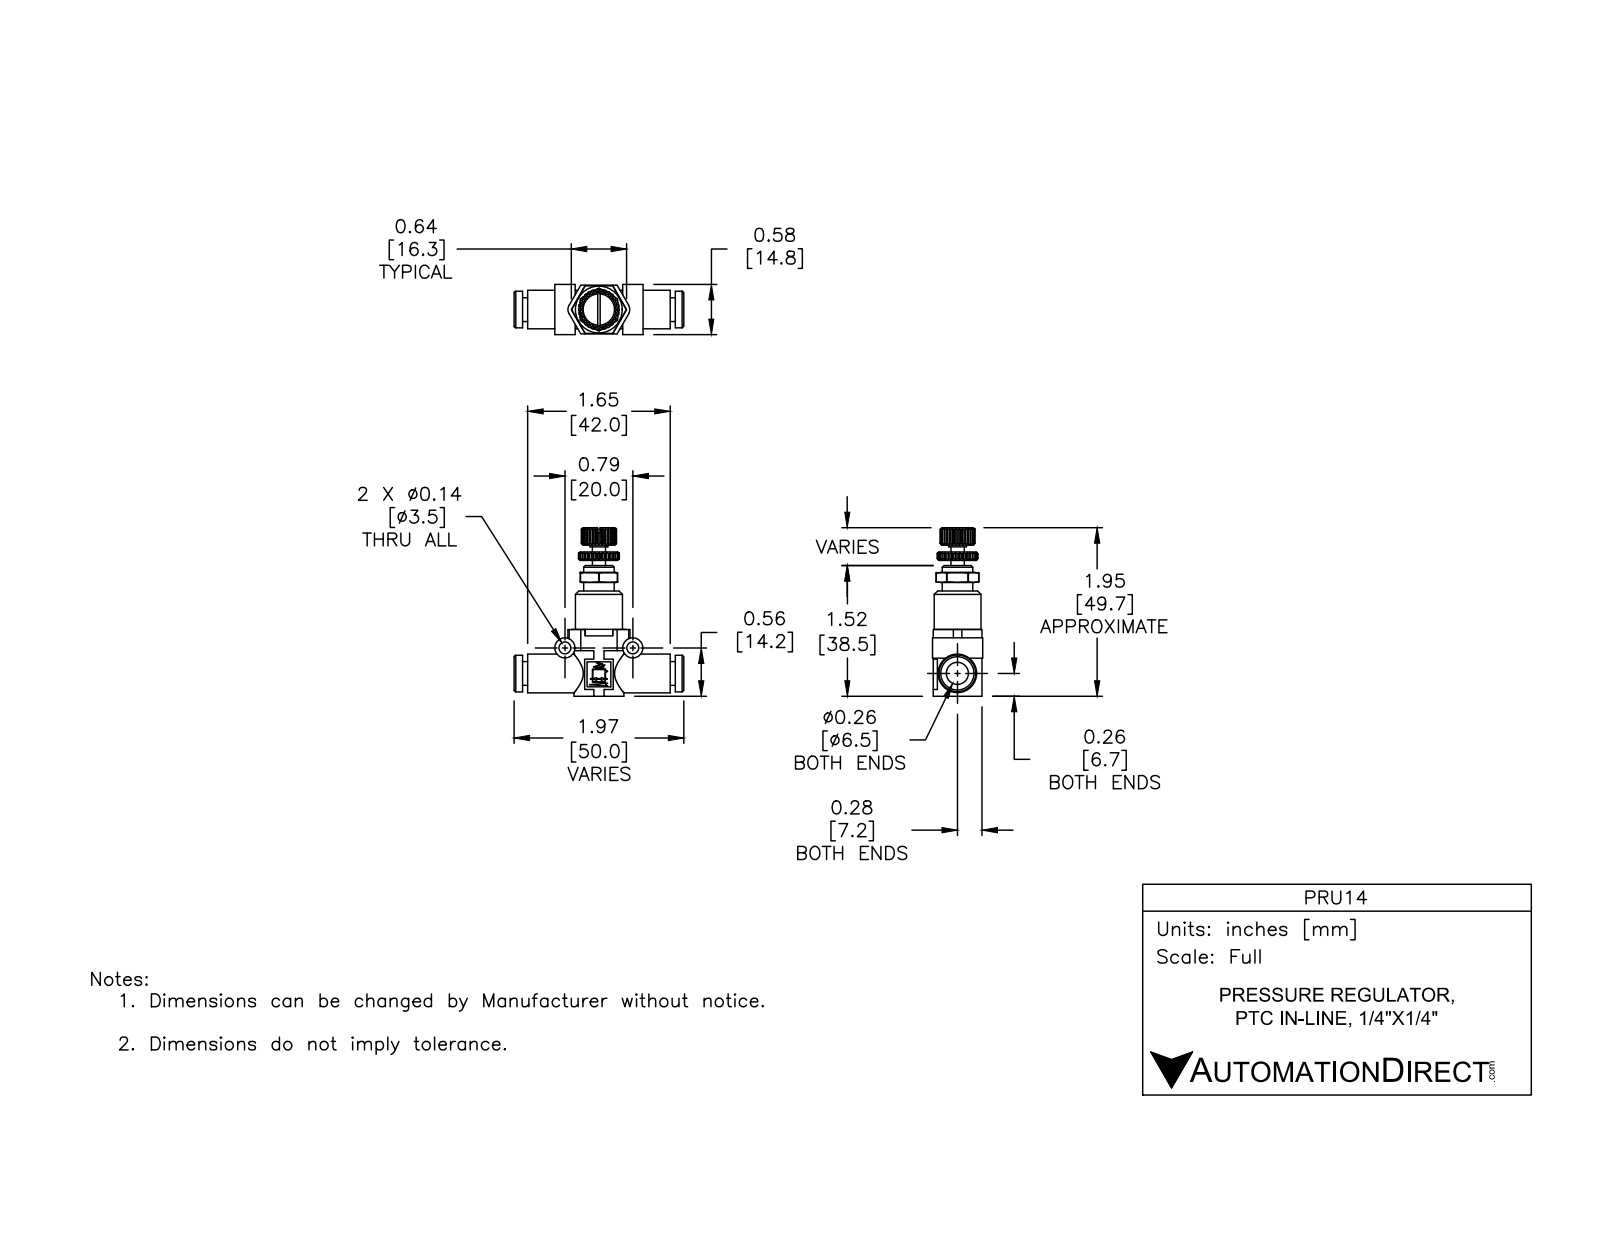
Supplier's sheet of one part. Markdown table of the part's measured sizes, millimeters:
| quantity | value |
| --- | --- |
| part name | PRU14 |
| STEP written by | SolidWorks 2015 (CONFIG_CONTROL_DESIGN) |
| units | millimeters |
| bodies | 4 solids, 389 faces (256 planar, 113 cylindrical, 20 other) |
| overall size | 50 × 49.65 × 14.8 |
| volume | 9 091 mm³ |
| surface area | 7 044 mm² |
| round holes (diameter × count) | 3.5 × 2, 6.5 × 1, 7.5 × 1 |
| round bosses / shafts (diameter × count) | 6 × 2, 14.65 × 1, 13.8 × 1, 11.4 × 1, 10.8 × 1, 9 × 1, 7 × 1, 5.25 × 1 |
| partial cylindrical surfaces (radius × count) | 2.5 × 2, 5.12 × 1, 6 × 1, 6.3 × 1 |
| main face-to-face distances | 2.5, 17.75, 1.5, 4, 43.5, 24.75, 14.34, 1.25, 42.5, 2 |
| hole center spacings | 20 |
